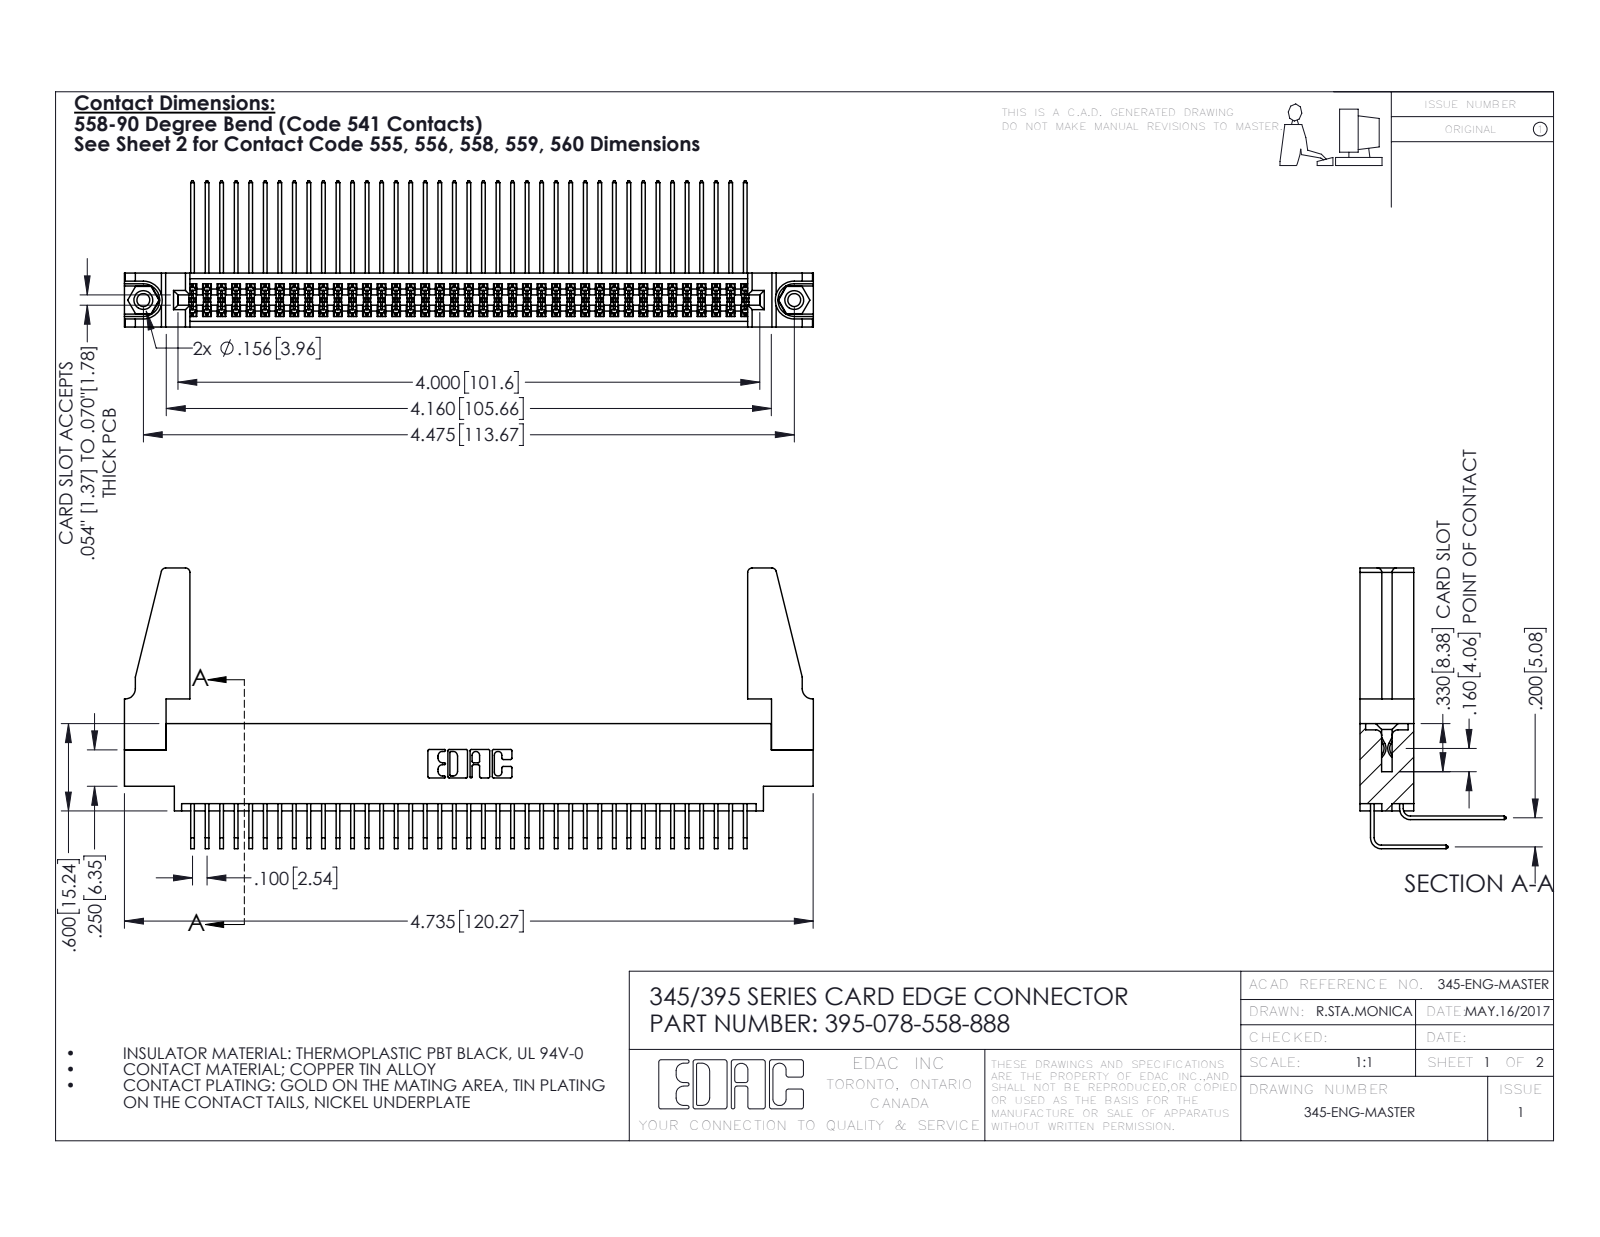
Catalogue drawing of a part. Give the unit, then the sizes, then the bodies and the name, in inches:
Units: inches
Overall size (bounding box): 4.736 × 1.929 × 1.005
Round holes (diameter × count): ⌀0.089 ×2, ⌀0.125 ×2, ⌀0.156 ×2, ⌀0.064 ×1
Round bosses / shafts (diameter × count): ⌀0.155 ×2
Partial cylindrical surfaces — rounded edges, fillets, slot ends (radius × count): R0.006 ×118, R0.01 ×22, R0.03 ×8, R0.007 ×6, R0.031 ×6, R0.026 ×3, R0.014 ×2, R0.019 ×2
Main face-to-face distances: 0.072, 0.298, 0.37, 0.2, 0.098, 0.272, 0.025, 0.225, 0.175, 0.025
Hole centre spacings: 0.27, 4.239, 4.475
Volume: 0.93 in³ · Surface area: 35.73 in²
Bodies: 83 solids, 4310 faces (2886 planar, 1408 cylindrical, 16 other)
Part name (STEP PRODUCT): 345-292-001_558 559 Tail - 1; 395-078-558-888; 345-220-078_345-220-088; 345-292-001_558 Tail - 2 (+2 more)
STEP written by: SolidWorks 2016 (CONFIG_CONTROL_DESIGN)
